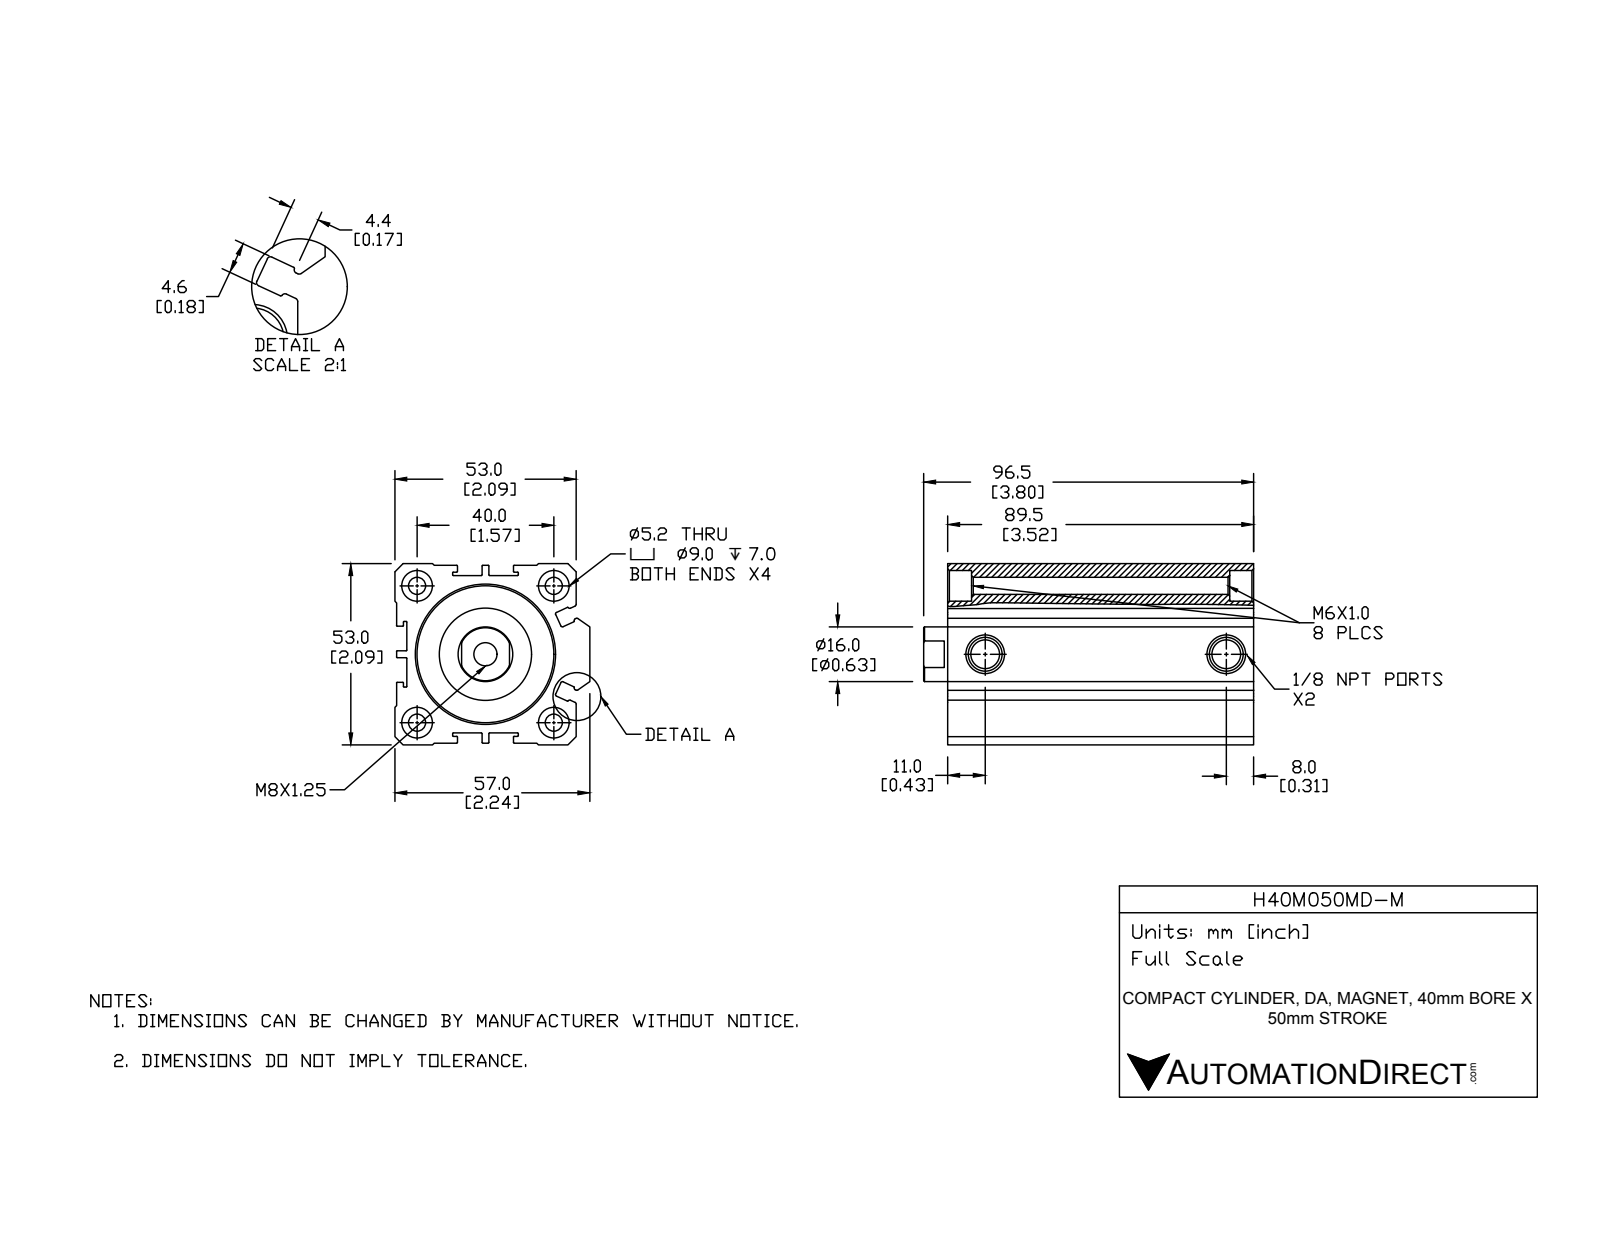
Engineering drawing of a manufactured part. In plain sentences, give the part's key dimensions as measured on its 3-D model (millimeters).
The part is named "H40M050MD-M-BODY; H40M050MD-M; H40M050MD-M-PISTON". Its 3-D file was written by "SolidWorks 2015 (CONFIG_CONTROL_DESIGN)". It is 2 solids with 255 faces: 99 planar, 103 cylindrical and 53 other. Overall it measures 96.5 by 57 by 53 millimeters. Its volume is 166 752 cubic millimeters and its surface area 59 248 square millimeters. Round holes: 4 of diameter 5, 4 of diameter 9, 2 of diameter 8.43, 1 of diameter 6.8, 1 of diameter 16, 1 of diameter 29.5, 1 of diameter 40. Round bosses or shafts: 1 of diameter 27, 1 of diameter 25. Partial cylindrical surfaces (rounded edges, fillets, slot ends): 40 of radius 0.2, 12 of radius 0.5. The main face-to-face distances are 3.5, 49.5, 0.5, 3, 52.5, 53, 49, 25, 46, 25.5. The hole center spacings are 28.28, 40, 56.57, 70.5.
